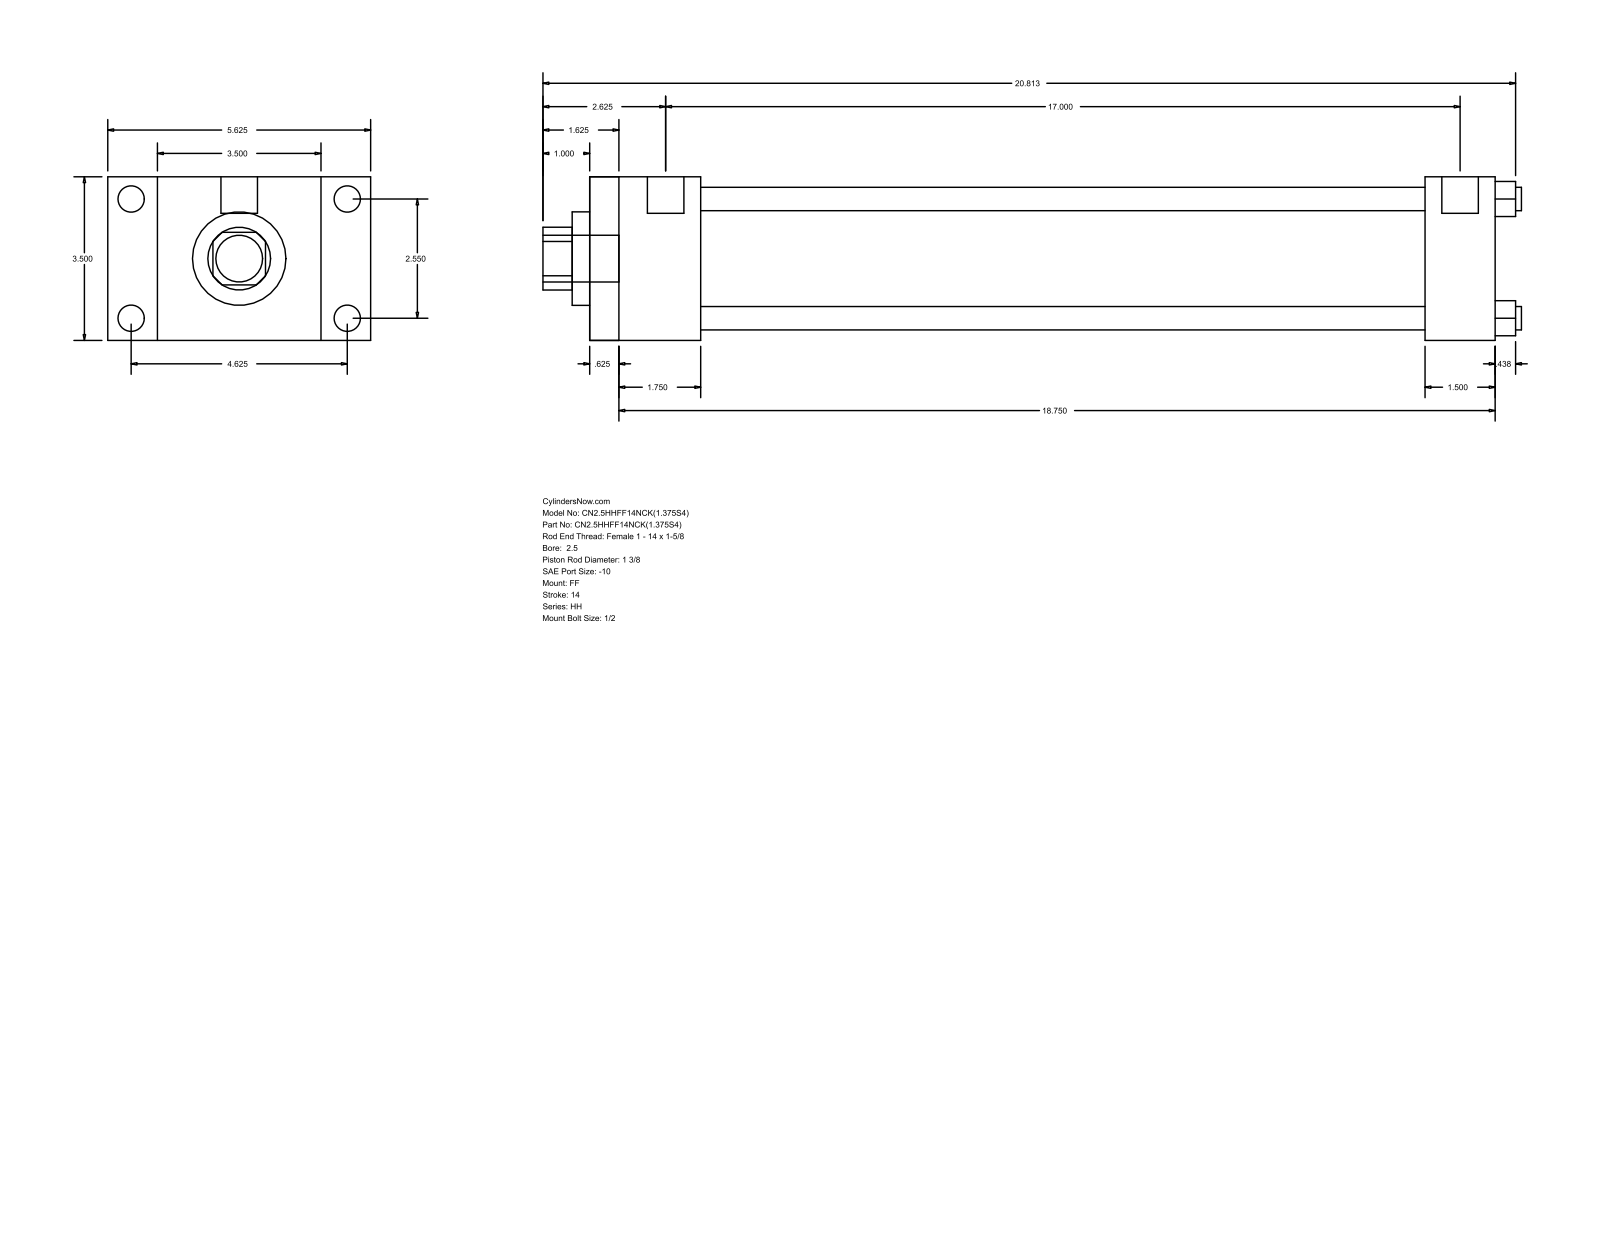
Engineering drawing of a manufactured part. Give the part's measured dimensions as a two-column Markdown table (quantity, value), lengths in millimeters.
| quantity | value |
| --- | --- |
| part name | HH_FF__0250_1.375 |
| STEP written by | GSSL Pune (CONFIG_CONTROL_DESIGN) |
| units | millimeters |
| bodies | 0 solids, 92 faces (64 planar, 28 cylindrical, 0 other) |
| overall size | 531.81 × 142.88 × 88.9 |
| round holes (diameter × count) | 12.7 × 4, 34.92 × 1, 50.8 × 1, 73.03 × 1 |
| round bosses / shafts (diameter × count) | 14.3 × 4, 5.56 × 4, 19.84 × 2, 25.4 × 1 |
| partial cylindrical surfaces (radius × count) | 17.06 × 1 |
| main face-to-face distances | 88.9, 492.12, 15.87, 476.25, 60.32, 44.45, 431.8, 454.03, 438.16, 393.71 |
| hole center spacings | 45.79, 64.76, 91.58 |
